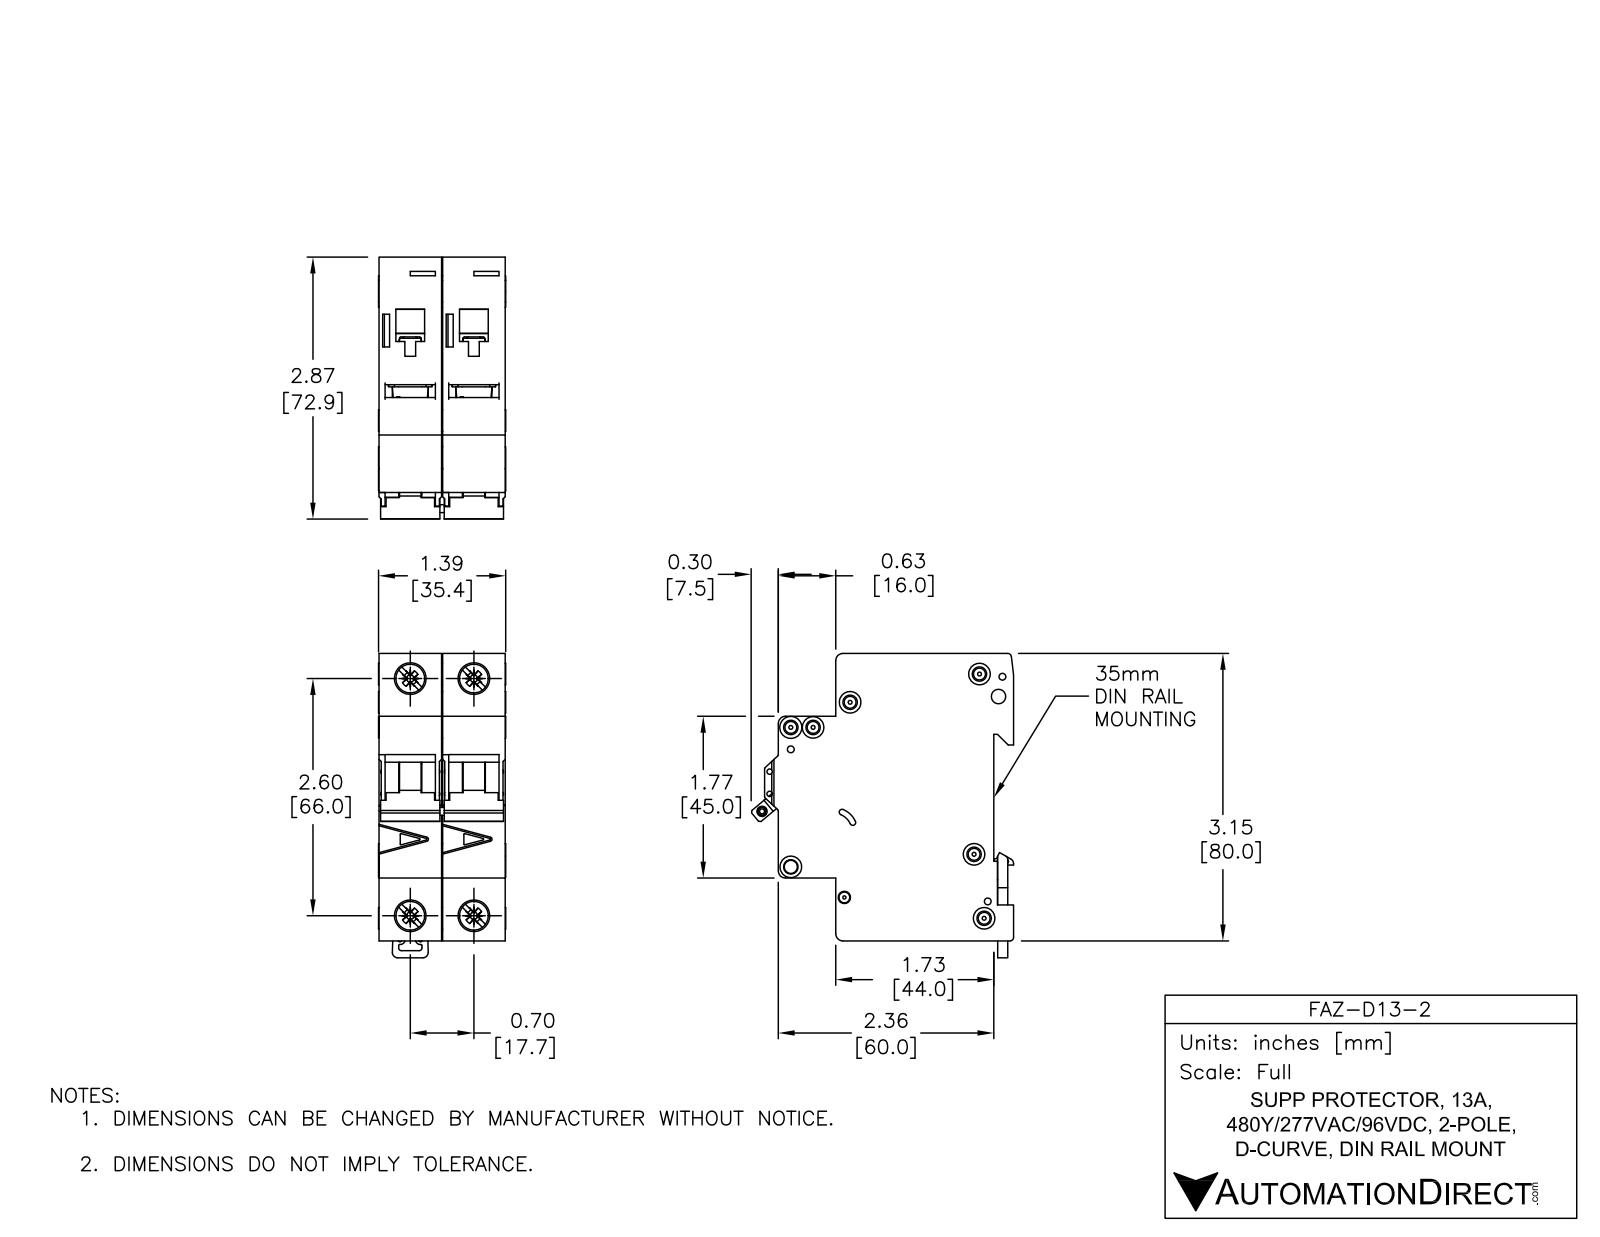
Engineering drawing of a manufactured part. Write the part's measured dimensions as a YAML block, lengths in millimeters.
part_name: "FAZ-D13-2"
step_written_by: "SolidWorks 2014 (AUTOMOTIVE_DESIGN)"
units: millimeters
bodies: {solids: 8, faces: 1104, planar: 466, cylindrical: 396, other: 242}
overall_size: [84.78, 73.04, 35.4]
volume: 149808
surface_area: 38799
round_holes:
  - {diameter: 3.6, count: 6}
  - {diameter: 1.9, count: 3}
  - {diameter: 1.09, count: 2}
  - {diameter: 1.5, count: 2}
  - {diameter: 4, count: 2}
  - {diameter: 7.15, count: 2}
  - {diameter: 8.2, count: 2}
  - {diameter: 2.15, count: 1}
  - {diameter: 2.2, count: 1}
  - {diameter: 2.55, count: 1}
  - {diameter: 3.3, count: 1}
  - {diameter: 3.4, count: 1}
round_bosses_or_shafts:
  - {diameter: 6, count: 4}
  - {diameter: 8.2, count: 2}
  - {diameter: 2.5, count: 2}
partial_cylinders:
  - {radius: 0.25, count: 49}
  - {radius: 0.5, count: 19}
  - {radius: 2, count: 10}
  - {radius: 0.2, count: 8}
  - {radius: 1, count: 8}
  - {radius: 0.8, count: 2}
  - {radius: 1.8, count: 2}
  - {radius: 3, count: 2}
face_to_face_distances: [17.7, 17.5, 35.2, 79.48, 5.5, 49.5, 44, 65.5, 60, 16]
hole_center_spacings: [6.2, 13.64, 17.7, 66, 68.33, 4.81, 5.19, 5.61]
